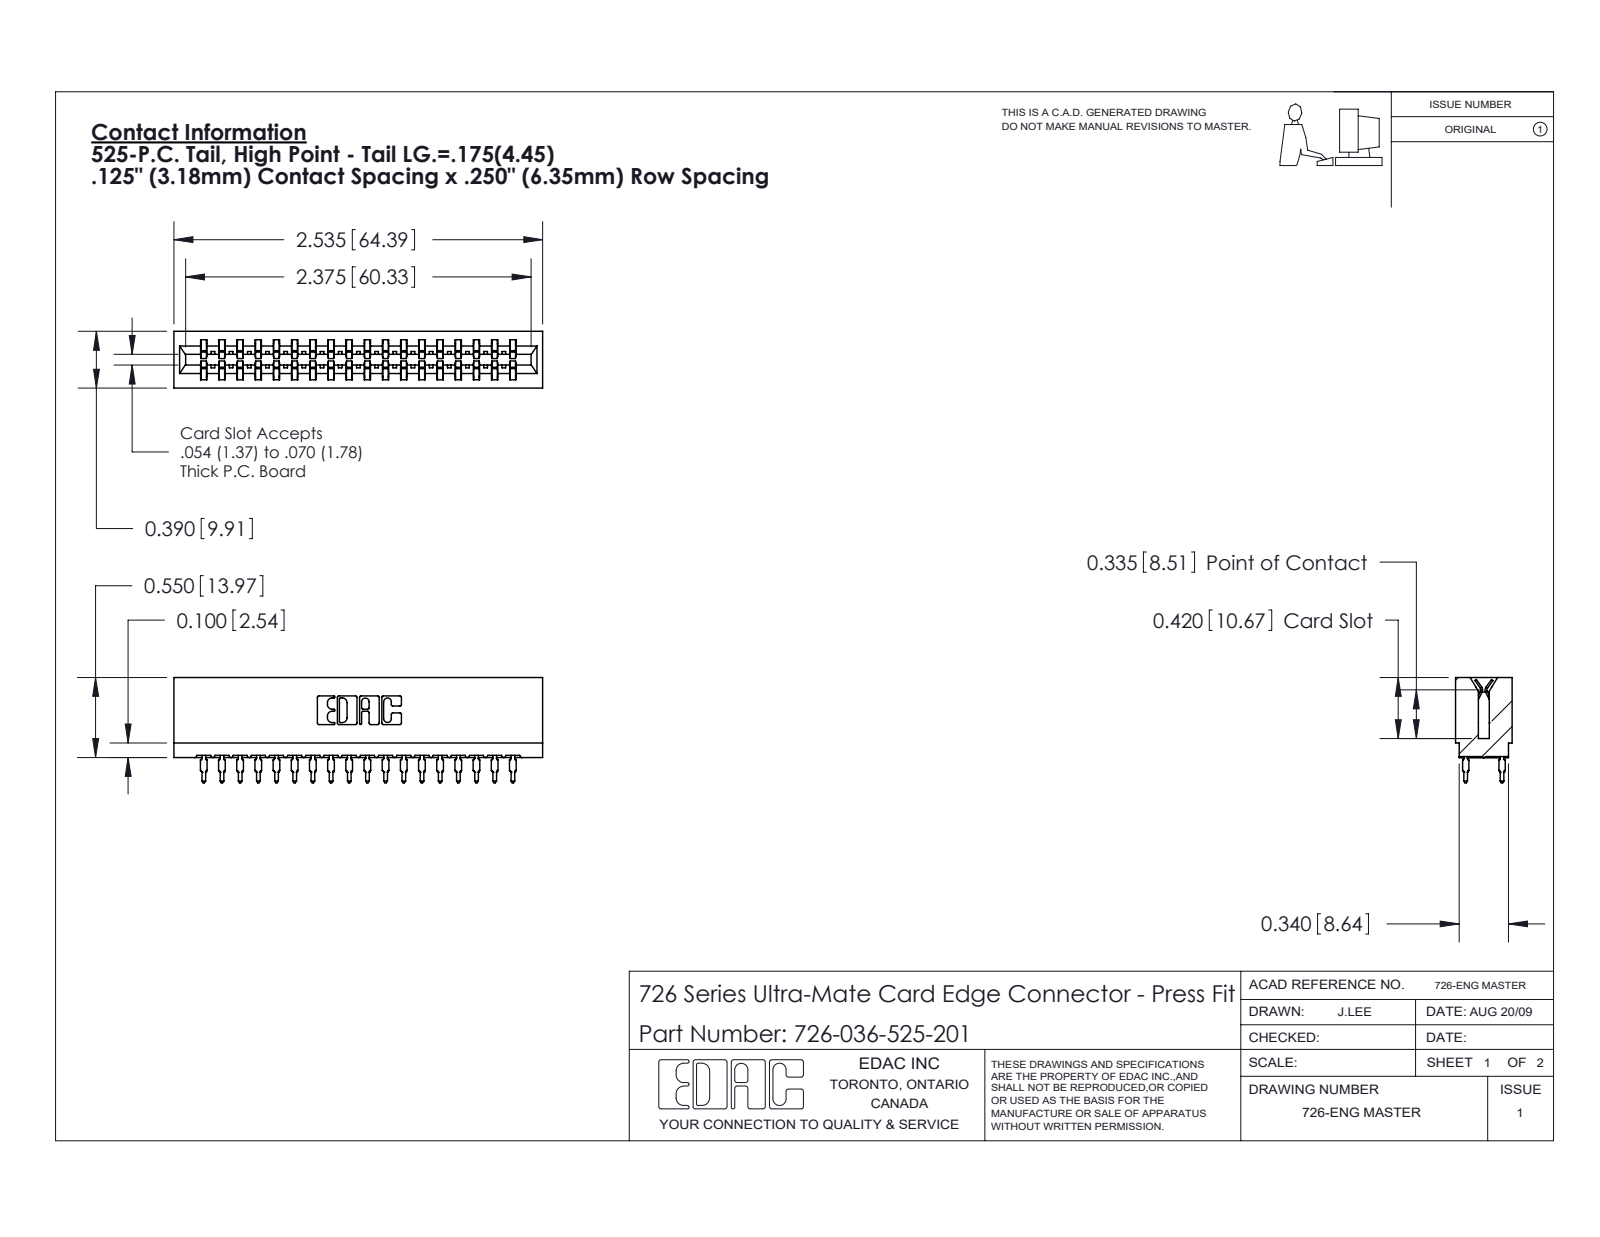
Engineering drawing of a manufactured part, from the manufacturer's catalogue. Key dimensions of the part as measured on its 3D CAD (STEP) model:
Part name (STEP PRODUCT): 726-036-525-201; 746-292-001_525; 726 Part_.515 Slot Depth - 01
STEP written by: SolidWorks 2020 (CONFIG_CONTROL_DESIGN)
Units: inches
Bodies: 37 solids, 3319 faces (1711 planar, 672 cylindrical, 936 other)
Overall size (bounding box): 2.535 × 0.724 × 0.39
Volume: 0.368 in³ · Surface area: 14.8 in²
Partial cylindrical surfaces — rounded edges, fillets, slot ends (radius × count): R0.021 ×72, R0.01 ×22, R0.015 ×19, R0.005 ×8, R0.011 ×8, R0.007 ×6, R0.031 ×6, R0.026 ×3
Main face-to-face distances: 0.057, 0.333, 0.39, 0.25, 0.025, 0.307, 0.083, 0.75, 0.5, 0.275
